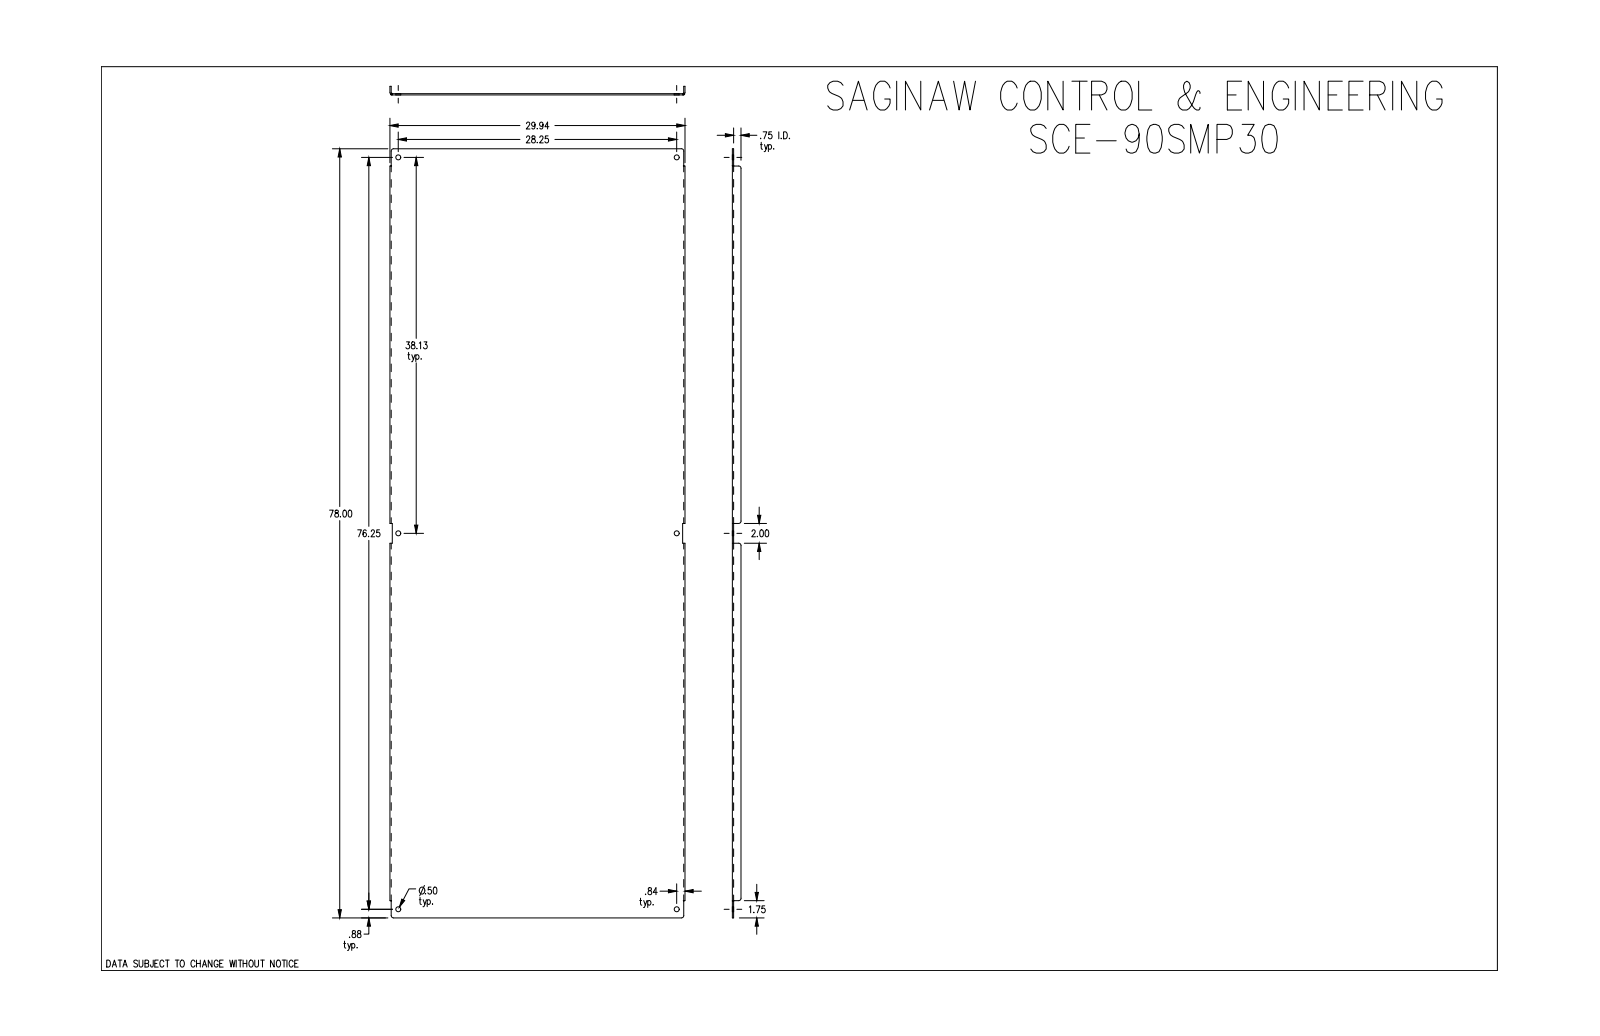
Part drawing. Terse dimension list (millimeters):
name: SCE-90SMP30
written by: SolidWorks 2019 (CONFIG_CONTROL_DESIGN)
unit: mm
bodies: 1 solid, 68 faces (30 planar, 26 cylindrical, 12 other)
size: 1981.2 × 760.4 × 22.2
volume: 4 977 000 mm³; area: 3 154 000 mm²
holes: 6× ⌀12.7
rounds: 8× R6.4, 2× R2.8, 2× R6
face distances: 3.2, 3.2, 757.3, 754, 760.4, 19.1, 22.2, 1981.2, 6, 754.4
hole spacings: 968.4, 1205.3, 717.6, 1936.8, 2065.4
